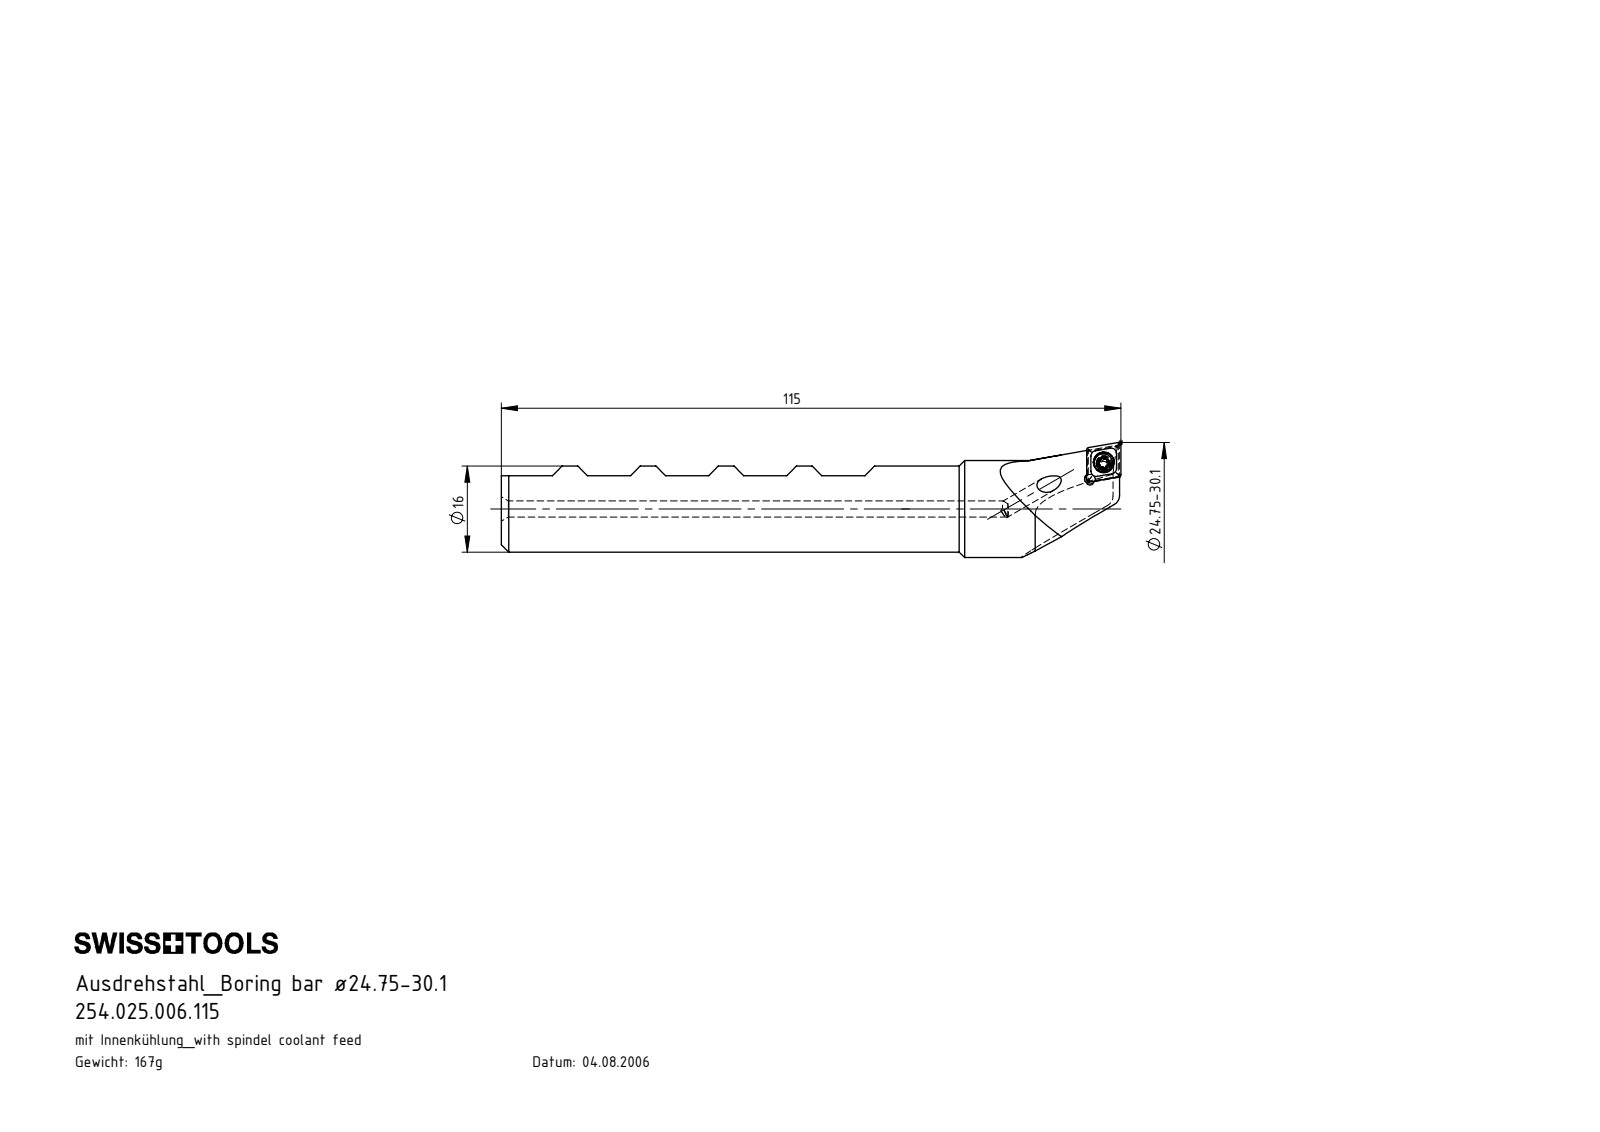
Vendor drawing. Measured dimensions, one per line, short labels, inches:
name: B25-WCA.K11.115_A; CCMT060204; B25.WCA.K11.115; WCA-ER2.001.006_A
written by: SolidWorks 2017 (AUTOMOTIVE_DESIGN)
unit: in
bodies: 3 solids, 110 faces (42 planar, 27 cylindrical, 41 other)
size: 4.528 × 0.842 × 0.745
volume: 1.296 in³; area: 11.3 in²
holes: 2× ⌀0.118, 1× ⌀0.079, 1× ⌀0.081, 1× ⌀0.11, 1× ⌀0.152
bosses: 1× ⌀0.709, 1× ⌀0.63, 1× ⌀0.134, 1× ⌀0.098
rounds: 6× R0.008, 5× R0.014, 1× R0.014, 1× R0.079, 1× R0.362, 1× R0.472
face distances: 0.404, 0.311, 0.807, 0.397, 0.086, 1.211, 0.807, 1.211, 0.404, 1.615
hole spacings: 0.153, 0.157
